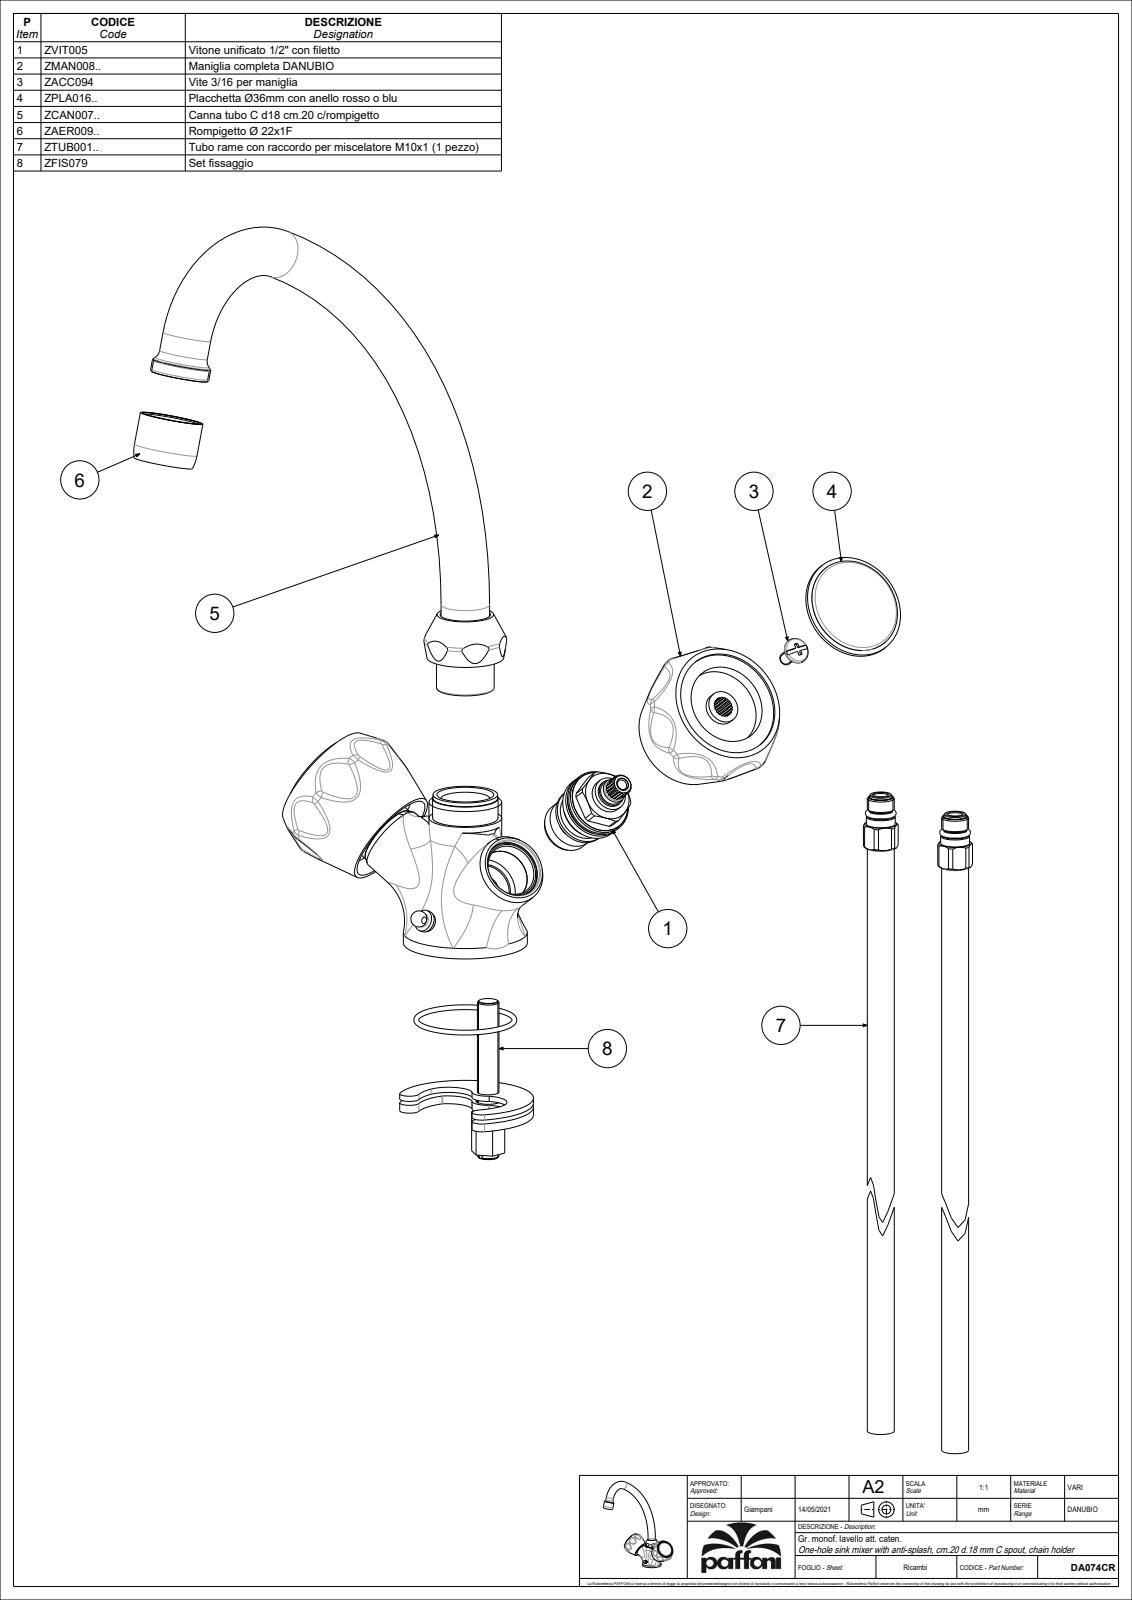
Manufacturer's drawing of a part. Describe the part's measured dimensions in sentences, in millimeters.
The part is named "DA074CR". Its 3-D file was written by "CREO PARAMETRIC BY PTC INC, 2020044 (CONFIG_CONTROL_DESIGN)". It is 1 solid with 373 faces: 40 planar, 100 cylindrical and 233 other. Overall it measures 235.5 by 186.96 by 145.89 millimeters. Its volume is 249 495 cubic millimeters and its surface area 56 350 square millimeters. Round holes: 4 of diameter 9, 2 of diameter 11, 2 of diameter 18, 2 of diameter 19, 2 of diameter 21.5, 2 of diameter 22, 1 of diameter 6, 1 of diameter 6.8, 1 of diameter 12, 1 of diameter 16.3, 1 of diameter 16.4, 1 of diameter 18.1. Round bosses or shafts: 2 of diameter 38.5, 2 of diameter 26, 2 of diameter 18, 1 of diameter 46, 1 of diameter 34, 1 of diameter 27, 1 of diameter 24, 1 of diameter 23.6. Partial cylindrical surfaces (rounded edges, fillets, slot ends): 16 of radius 21.31, 1 of radius 18.5. The main face-to-face distances are 35.3, 0.4, 35.7, 56, 55.6, 20.3, 1.3, 66.16, 64.86, 55. The hole center spacings are 7, 13.89, 12, 14.
